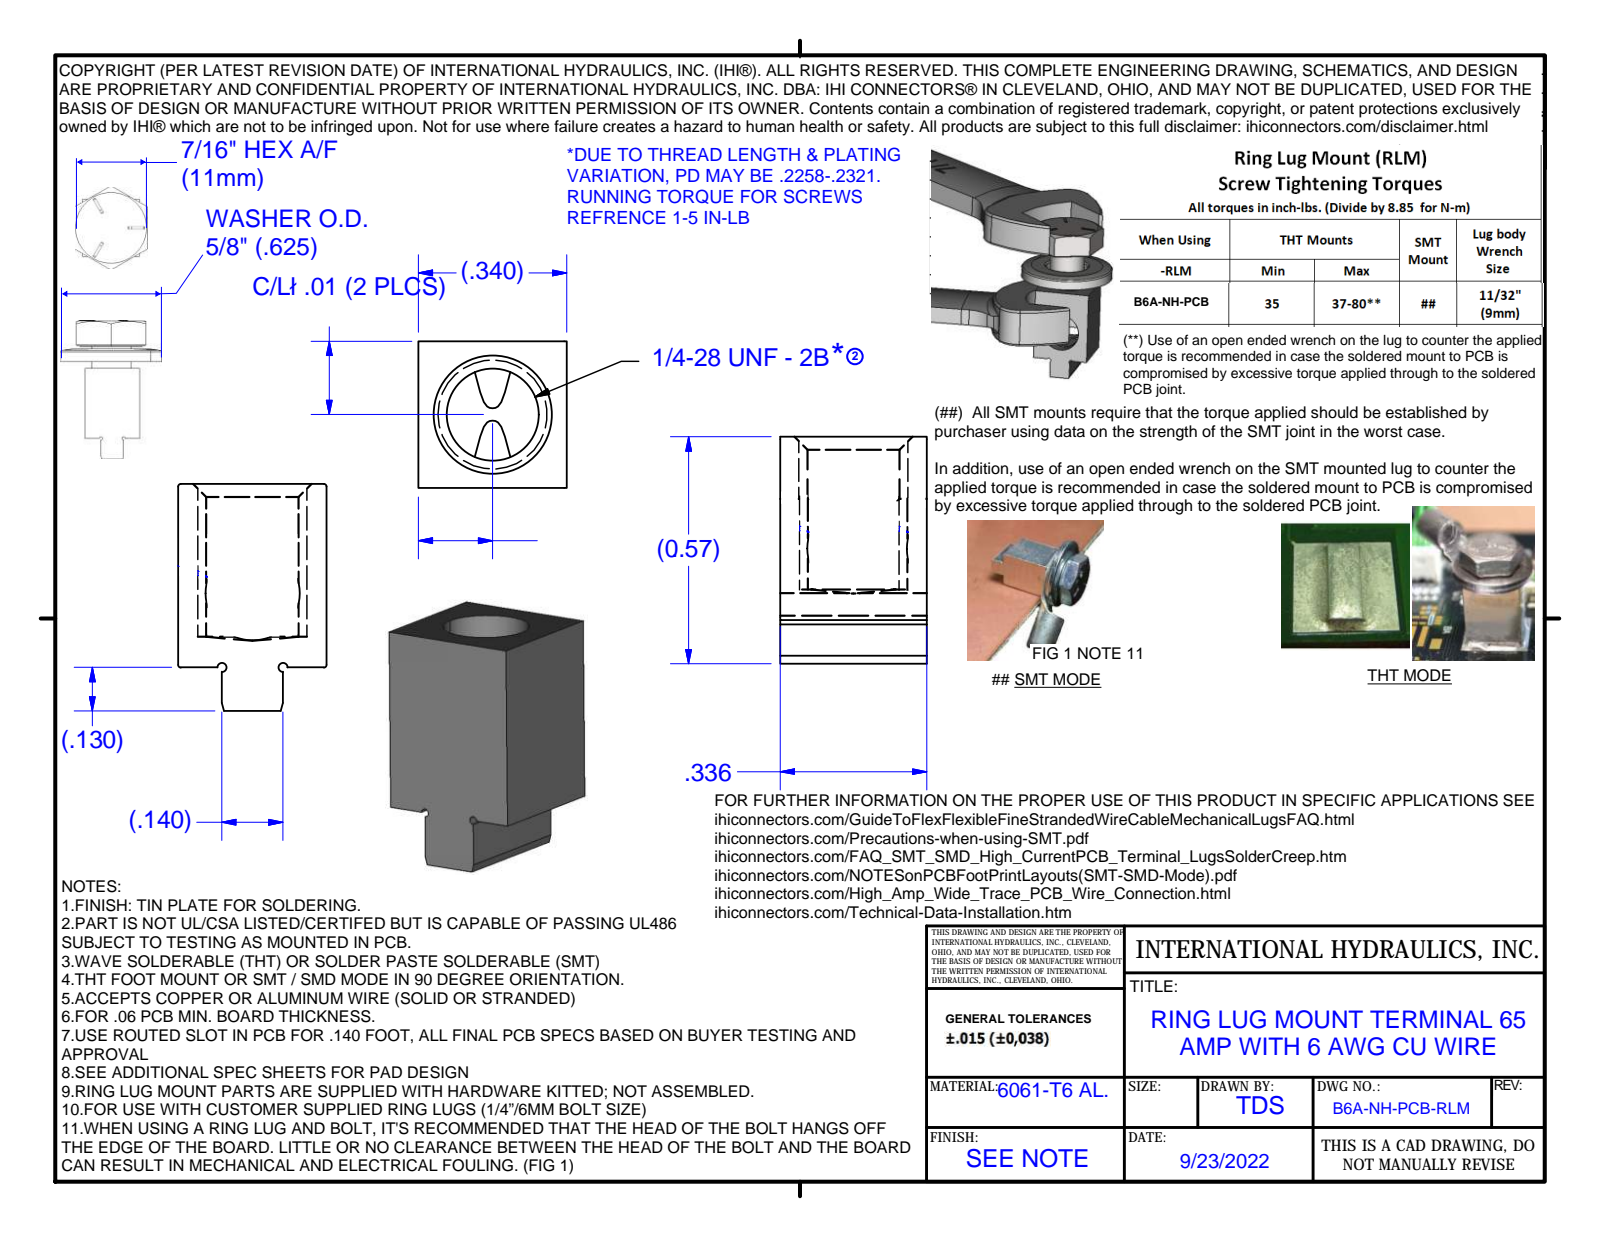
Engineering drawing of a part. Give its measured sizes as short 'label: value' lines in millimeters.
name: B6A-NH-PCB-28; 25NWSA0T; 25F37HCS5T
written by: FreeCAD (AUTOMOTIVE_DESIGN)
unit: mm
bodies: 3 solids, 97 faces (46 planar, 31 cylindrical, 20 other)
size: 21.12 × 16.13 × 16.13
volume: 1 744 mm³; area: 1 748 mm²
holes: 1× ⌀5.36, 1× ⌀7.49
bosses: 1× ⌀16.13, 1× ⌀9.91, 1× ⌀6.22
rounds: 12× R0.13, 2× R0.25
face distances: 8.53, 8.64, 6.48, 2.03, 4.45, 2.54, 2.07, 6.52, 0.38, 2.45
